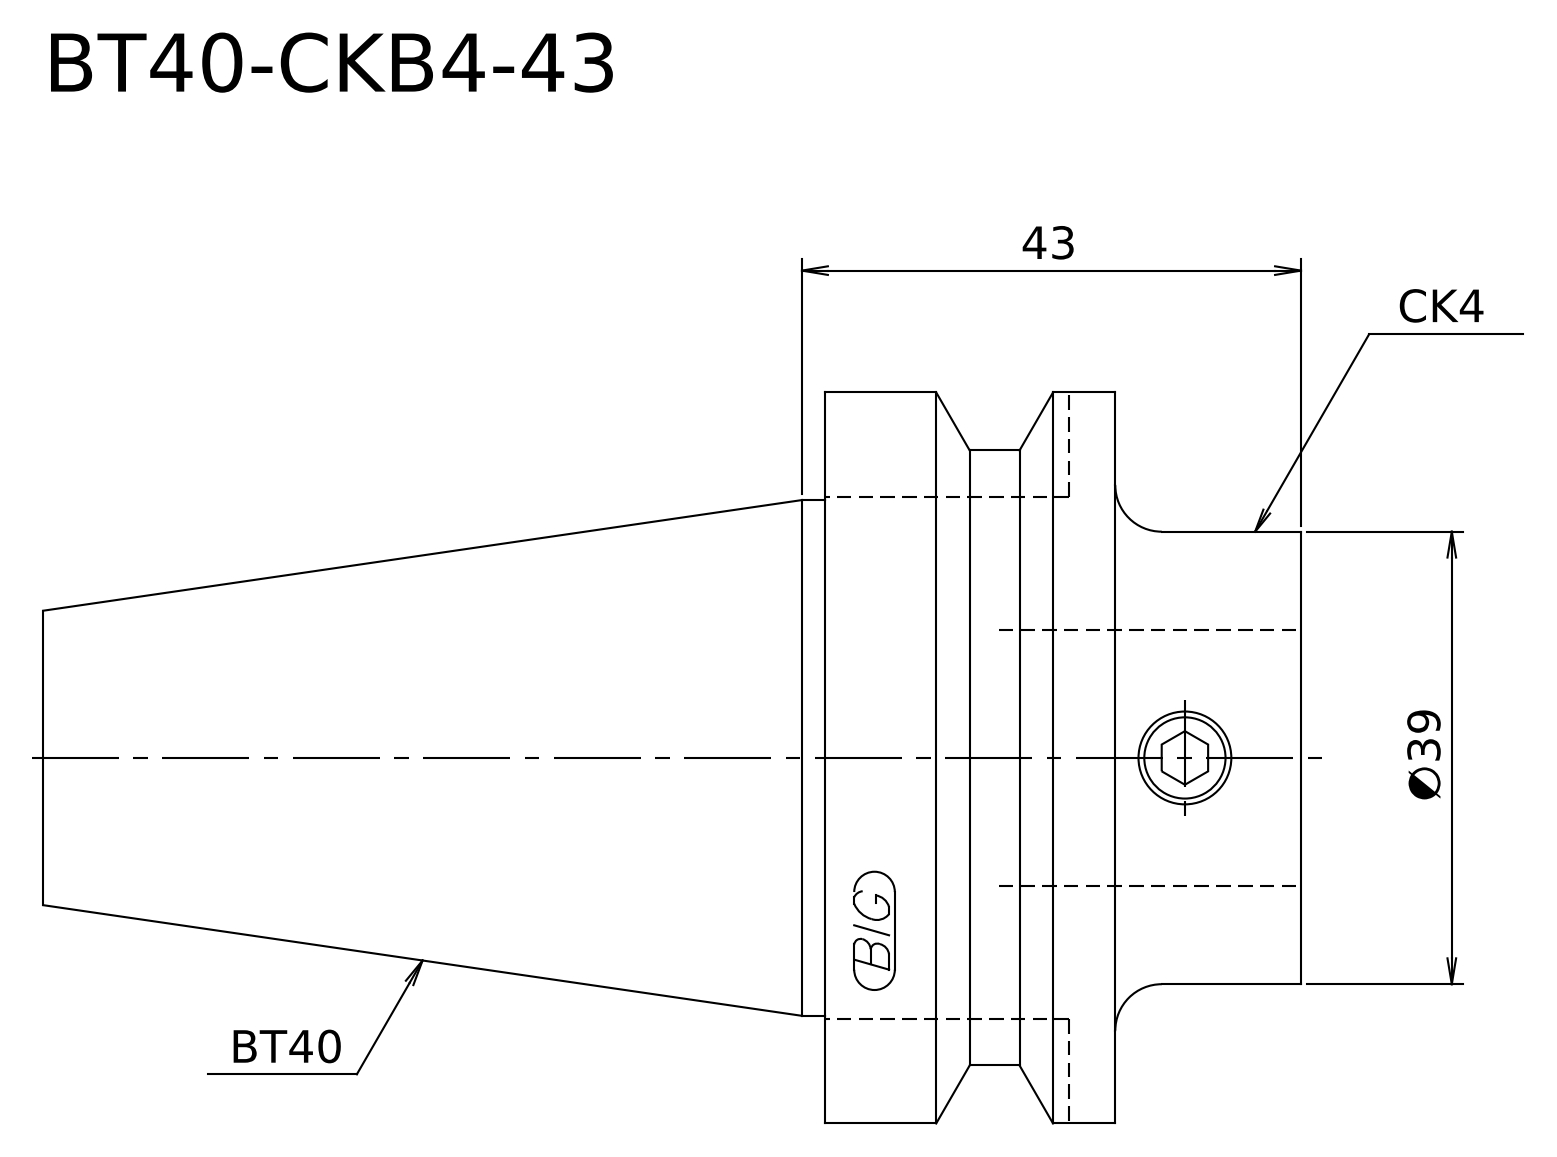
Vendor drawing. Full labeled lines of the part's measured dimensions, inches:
STEP written by: Kubotek KeyCreator V8.5.1 (14335) (CONFIG_CONTROL_DESIGN)
Units: inches
Bodies: 1 solid, 14 faces (4 planar, 5 cylindrical, 5 other)
Overall size (bounding box): 4.268 × 2.48 × 2.48
Volume: 9.726 in³ · Surface area: 31.11 in²
Round bosses / shafts (diameter × count): ⌀2.48 ×1, ⌀2.087 ×1, ⌀1.75 ×1, ⌀1.535 ×1
Main face-to-face distances: 0.984, 0.63, 1.614, 4.268, 3.638, 2.654
